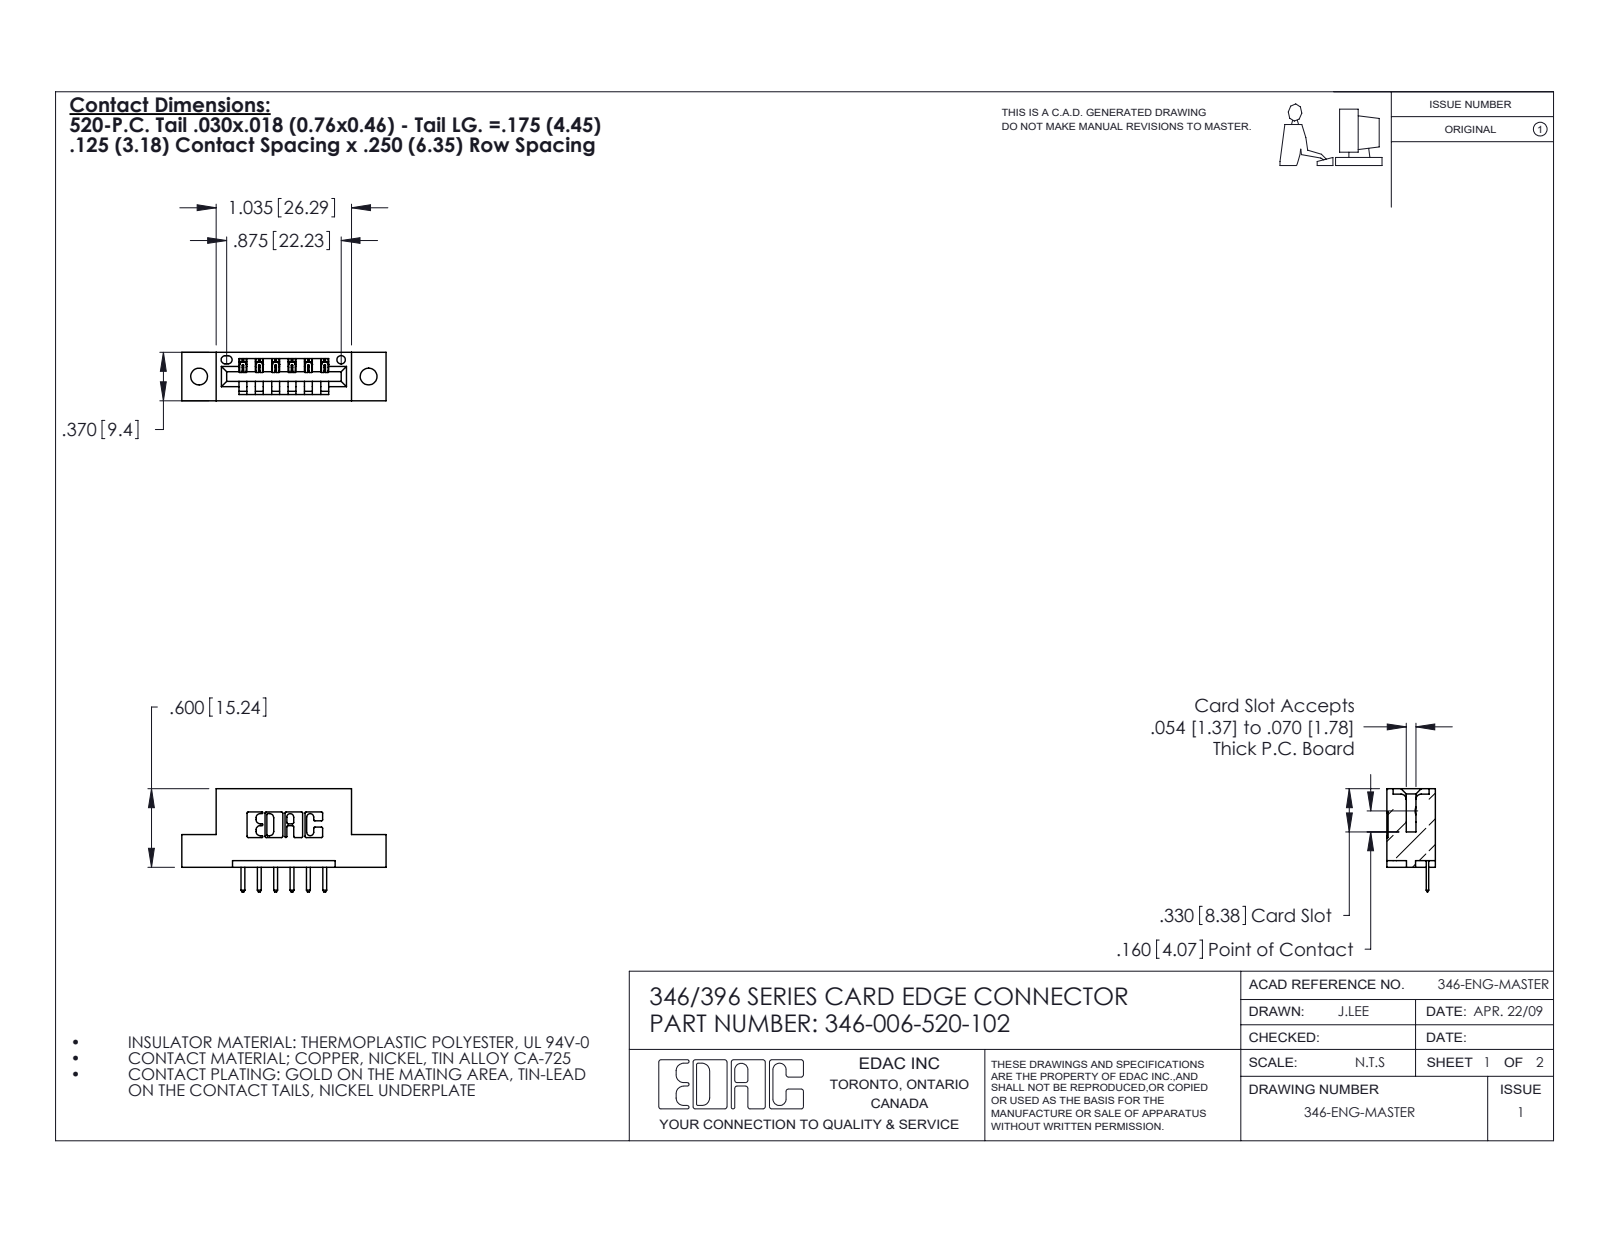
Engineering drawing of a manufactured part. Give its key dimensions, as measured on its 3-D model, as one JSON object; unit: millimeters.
{"part_name": "346-006-520-102; 345-292-001_345-293-120; 346 Part_Flush Mounting Lugs - 0.128 Dia", "step_written_by": "SolidWorks 2020 (CONFIG_CONTROL_DESIGN)", "units": "millimeters", "bodies": {"solids": 7, "faces": 494, "planar": 328, "cylindrical": 166, "other": 0}, "overall_size": [39.6, 20, 9.4], "volume_mm3": 3490, "surface_area_mm2": 3646, "round_holes": [[3.3, 2], [1.6, 1]], "partial_cylinders_radius": [[0.3, 22], [0.3, 14], [0.2, 12], [0.2, 6], [0.8, 6], [0.7, 3], [0.8, 2], [1, 2]], "face_to_face_distances": [6.4, 9.4, 1.2, 8.2, 3.8, 5.6, 2.5, 4.4, 3.2, 3.2], "hole_center_spacings": [6.2, 27.7, 32.9]}
